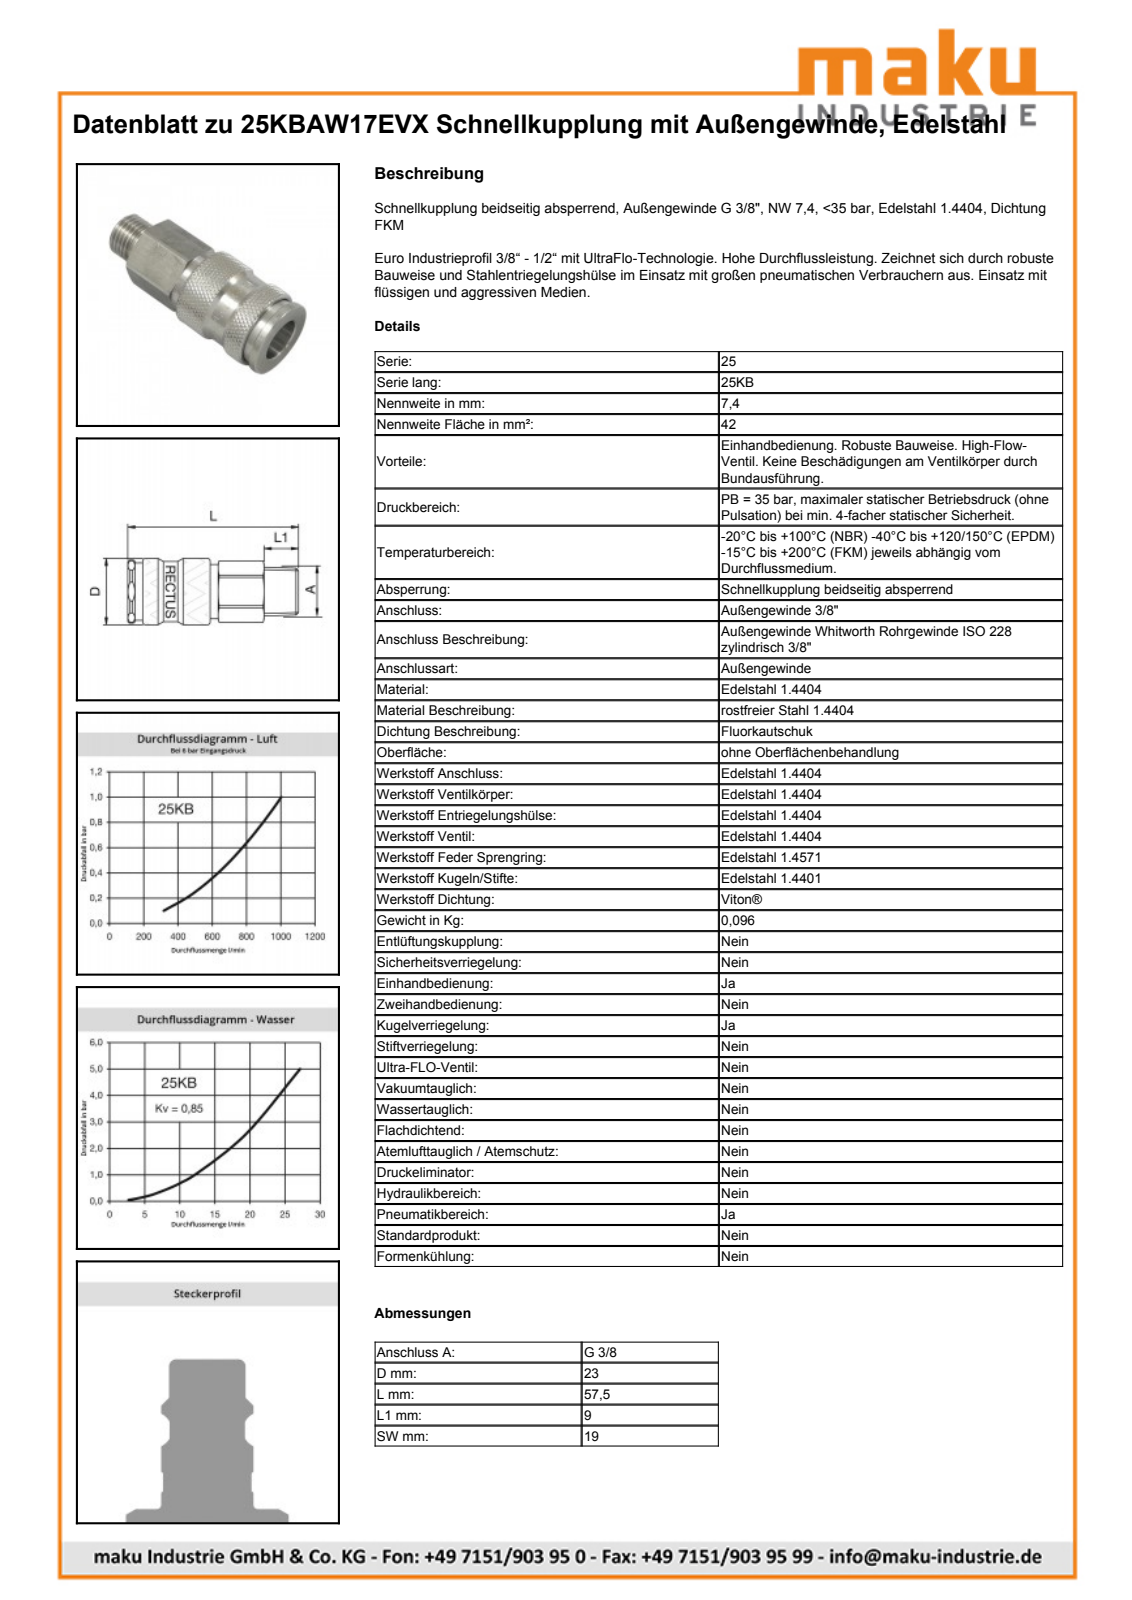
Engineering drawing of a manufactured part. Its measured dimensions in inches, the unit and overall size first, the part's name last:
Units: inches
Overall size (bounding box): 2.262 × 0.911 × 0.911
Round holes (diameter × count): ⌀0.679 ×1, ⌀0.762 ×1, ⌀0.789 ×1
Round bosses / shafts (diameter × count): ⌀0.911 ×1, ⌀0.866 ×1, ⌀0.827 ×1, ⌀0.787 ×1, ⌀0.746 ×1, ⌀0.656 ×1, ⌀0.63 ×1
Partial cylindrical surfaces — rounded edges, fillets, slot ends (radius × count): R0.277 ×1, R0.409 ×1, R0.421 ×1
Main face-to-face distances: 0.748, 2.262, 0.963, 1.299, 1.132, 0.169, 1.13, 1.907, 0.945, 0.776
Volume: 1.082 in³ · Surface area: 11.88 in²
Bodies: 2 solids, 594 faces (236 planar, 77 cylindrical, 281 other)
Part name (STEP PRODUCT): D105166
STEP written by: Autodesk Inventor 2011 (AUTOMOTIVE_DESIGN)
